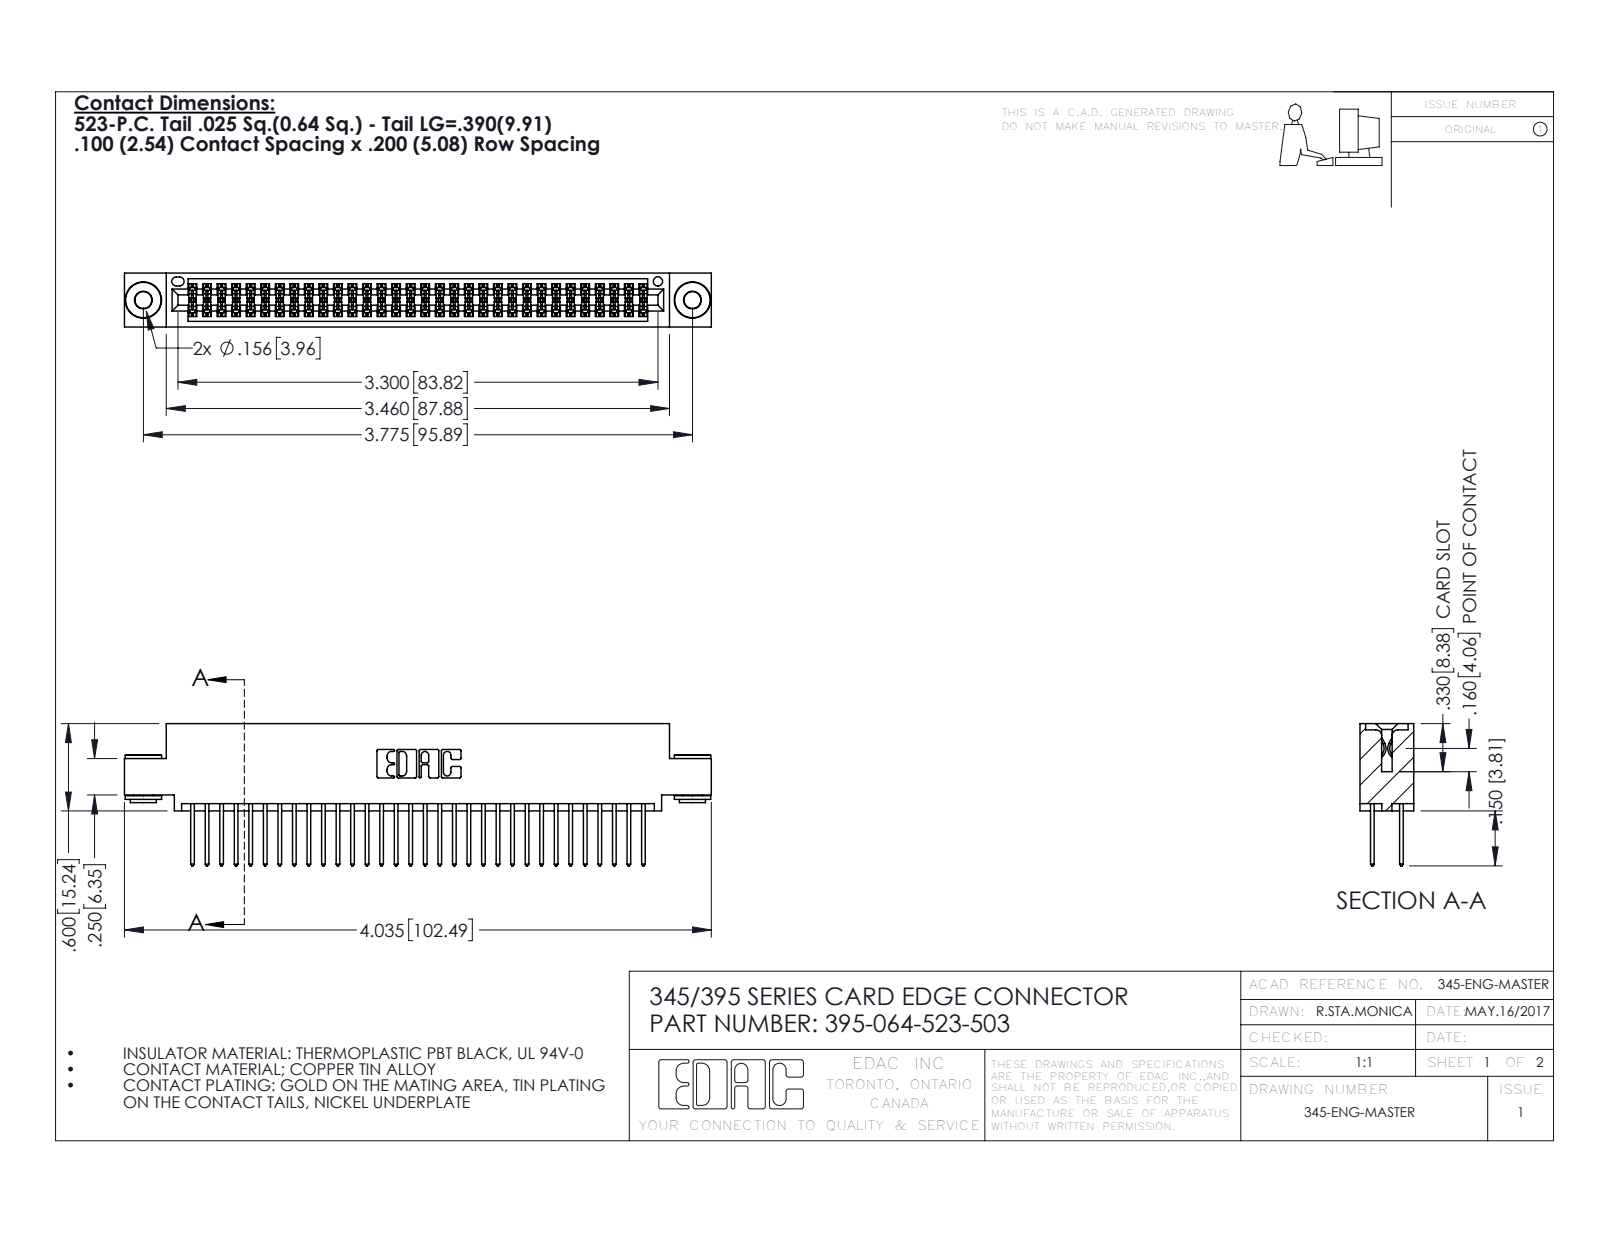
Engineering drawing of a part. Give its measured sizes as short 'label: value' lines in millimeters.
name: 345-292-001_345-293-123; 395-064-523-503; 345-250-002_345-250-002-102; 345 Part_0.110 Offset - 0.156 Dia-TH
written by: SolidWorks 2016 (CONFIG_CONTROL_DESIGN)
unit: mm
bodies: 67 solids, 3368 faces (2206 planar, 1154 cylindrical, 8 other)
size: 102.5 × 24.8 × 9.4
volume: 9 950 mm³; area: 15 390 mm²
holes: 2× ⌀2.9, 2× ⌀4, 1× ⌀1.6
bosses: 2× ⌀6.4, 2× ⌀4.6, 2× ⌀3.5
rounds: 96× R0.2, 64× R0.3, 22× R0.3, 6× R0.2, 6× R0.8, 3× R0.7, 2× R0.4, 2× R0.5
face distances: 1.8, 7.6, 5.1, 0.6, 2.5, 6.9, 9.4, 5.7, 4.4, 3.8
hole spacings: 6.9, 89.9, 95.9
